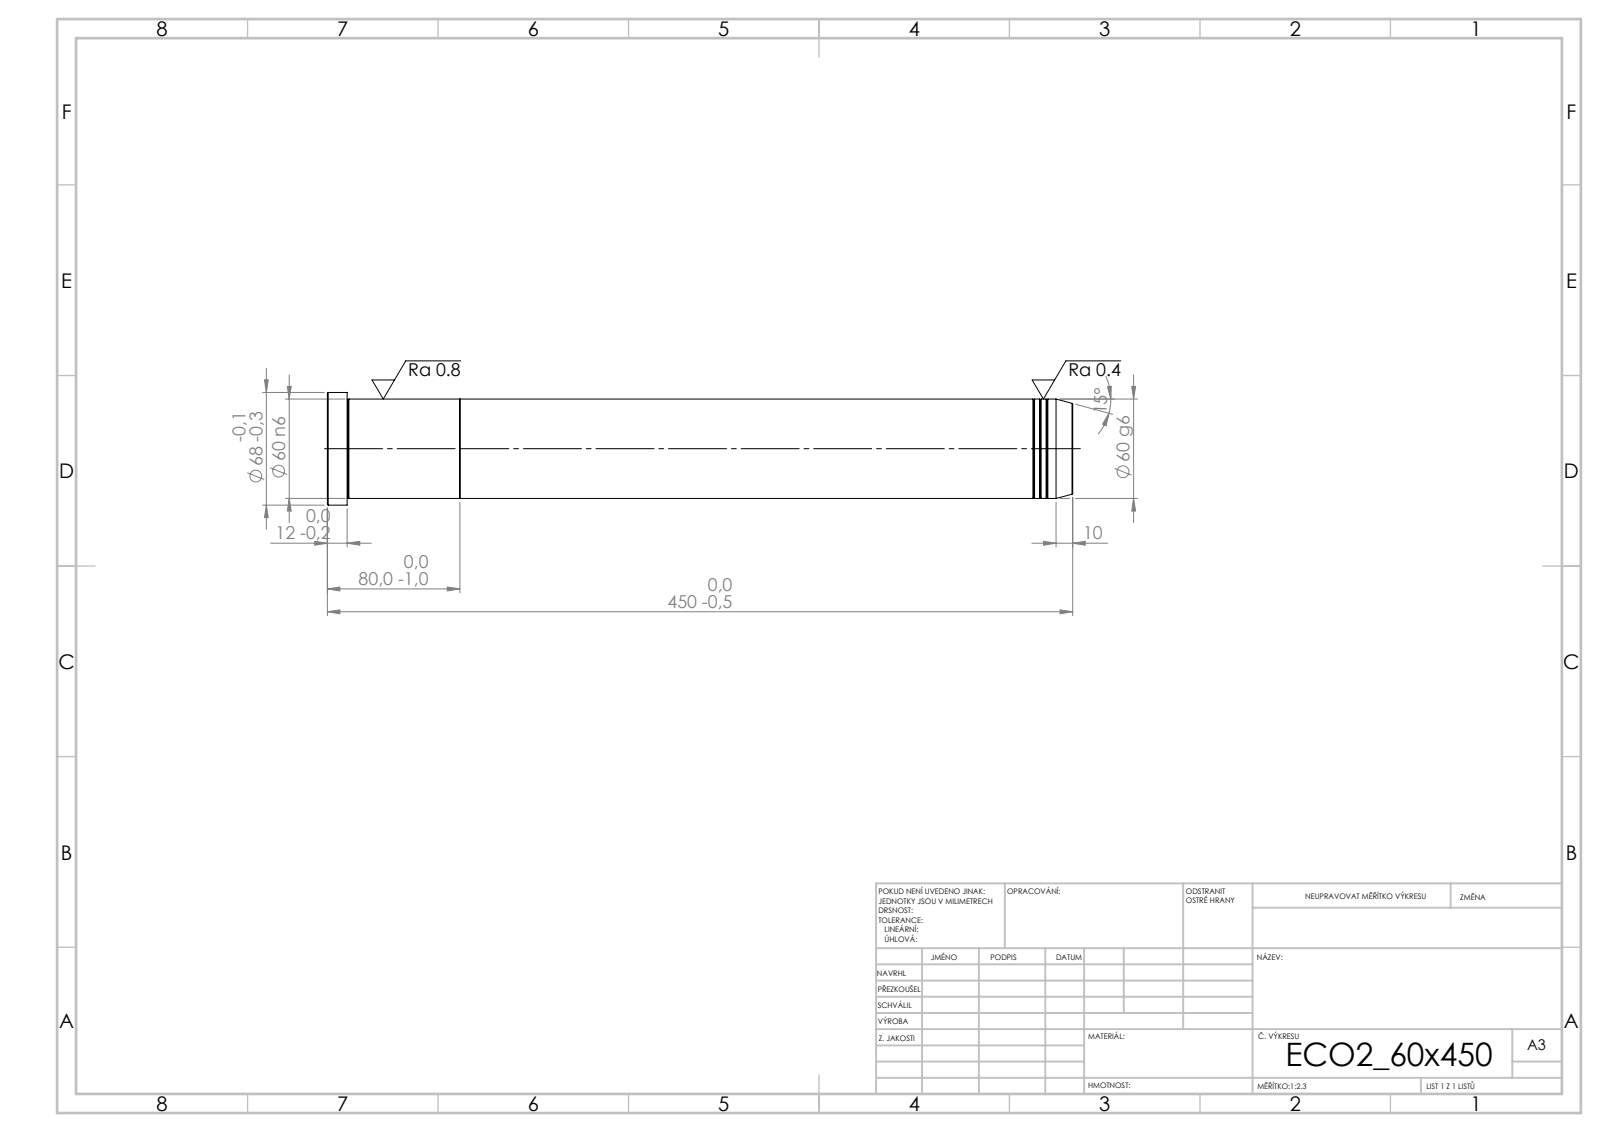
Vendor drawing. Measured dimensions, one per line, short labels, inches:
written by: SolidWorks 2019 (CONFIG_CONTROL_DESIGN)
unit: in
bodies: 2 solids, 39 faces (5 planar, 12 cylindrical, 22 other)
size: 17.717 × 2.677 × 2.677
volume: 78.05 in³; area: 151.7 in²
bosses: 1× ⌀2.677, 1× ⌀2.362
face distances: 3.15, 14.567, 17.717, 17.244, 2.677, 0.472
